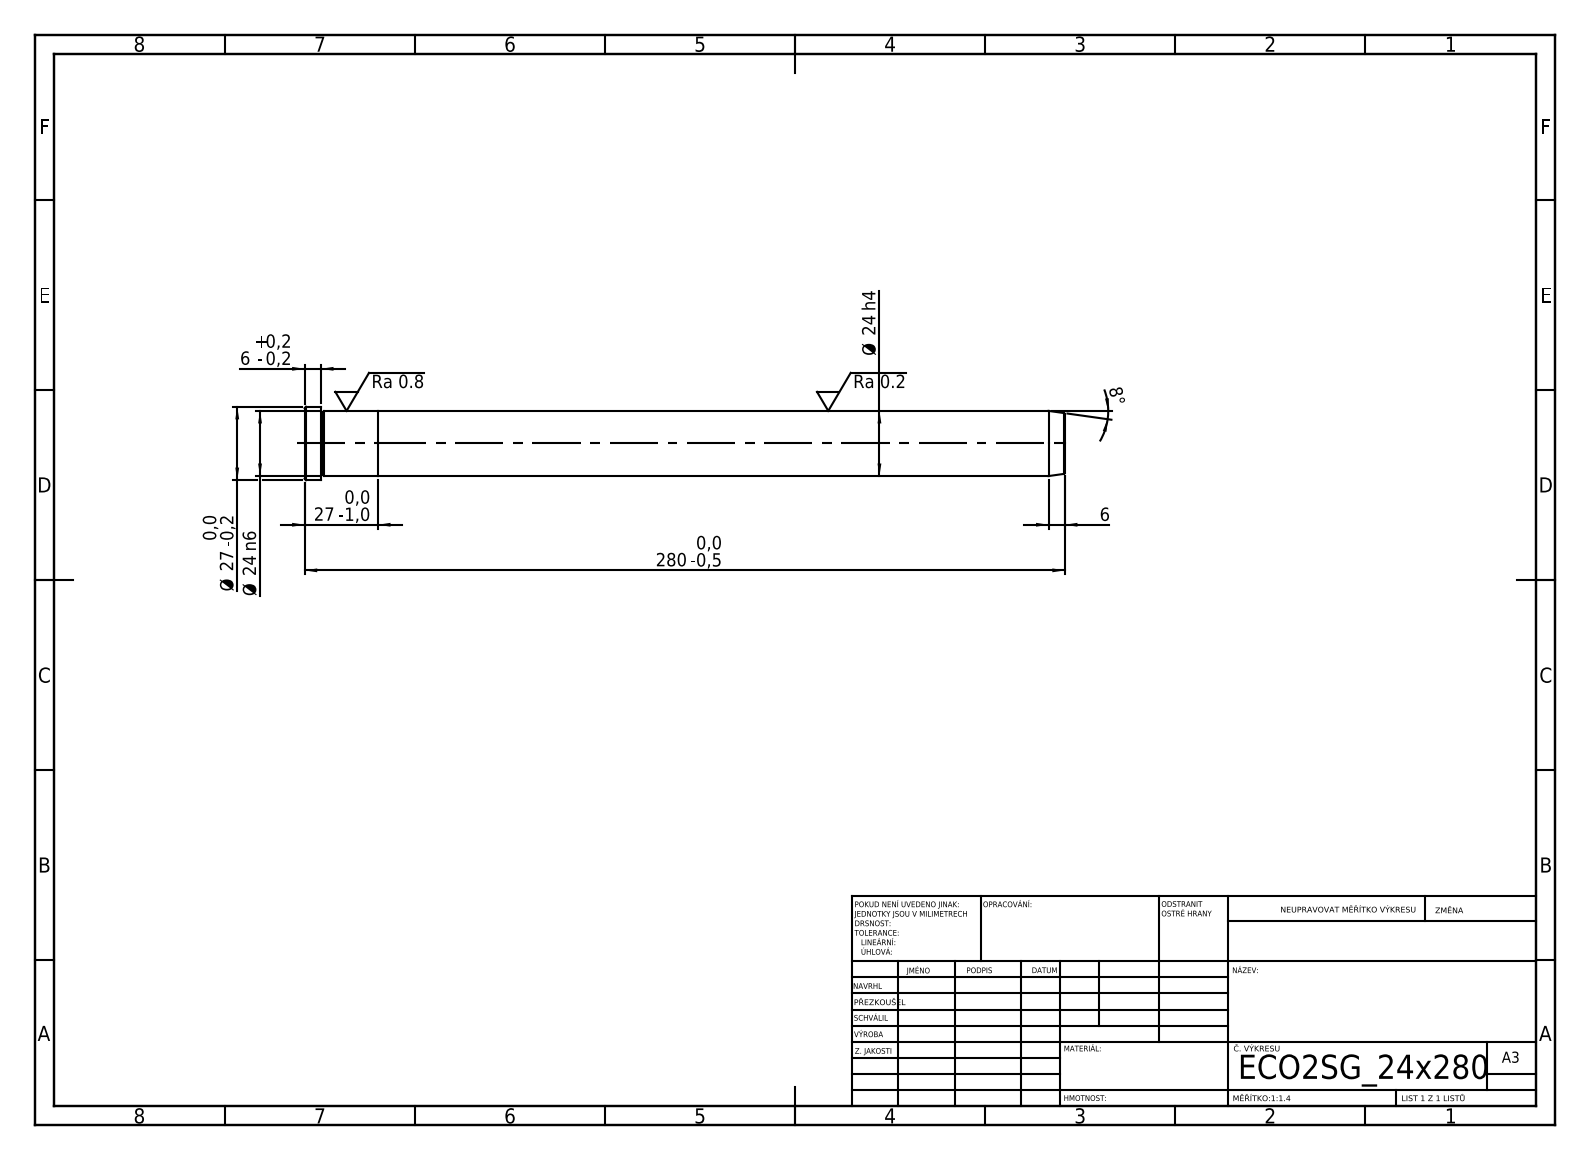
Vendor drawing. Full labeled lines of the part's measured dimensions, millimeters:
STEP written by: SolidWorks 2019 (CONFIG_CONTROL_DESIGN)
Units: millimetres
Bodies: 2 solids, 21 faces (5 planar, 6 cylindrical, 10 other)
Overall size (bounding box): 280 × 27 × 27
Volume: 127 162 mm³ · Surface area: 23 149 mm²
Round bosses / shafts (diameter × count): ⌀27 ×1, ⌀24 ×1
Main face-to-face distances: 27, 253, 280, 274, 21, 6
